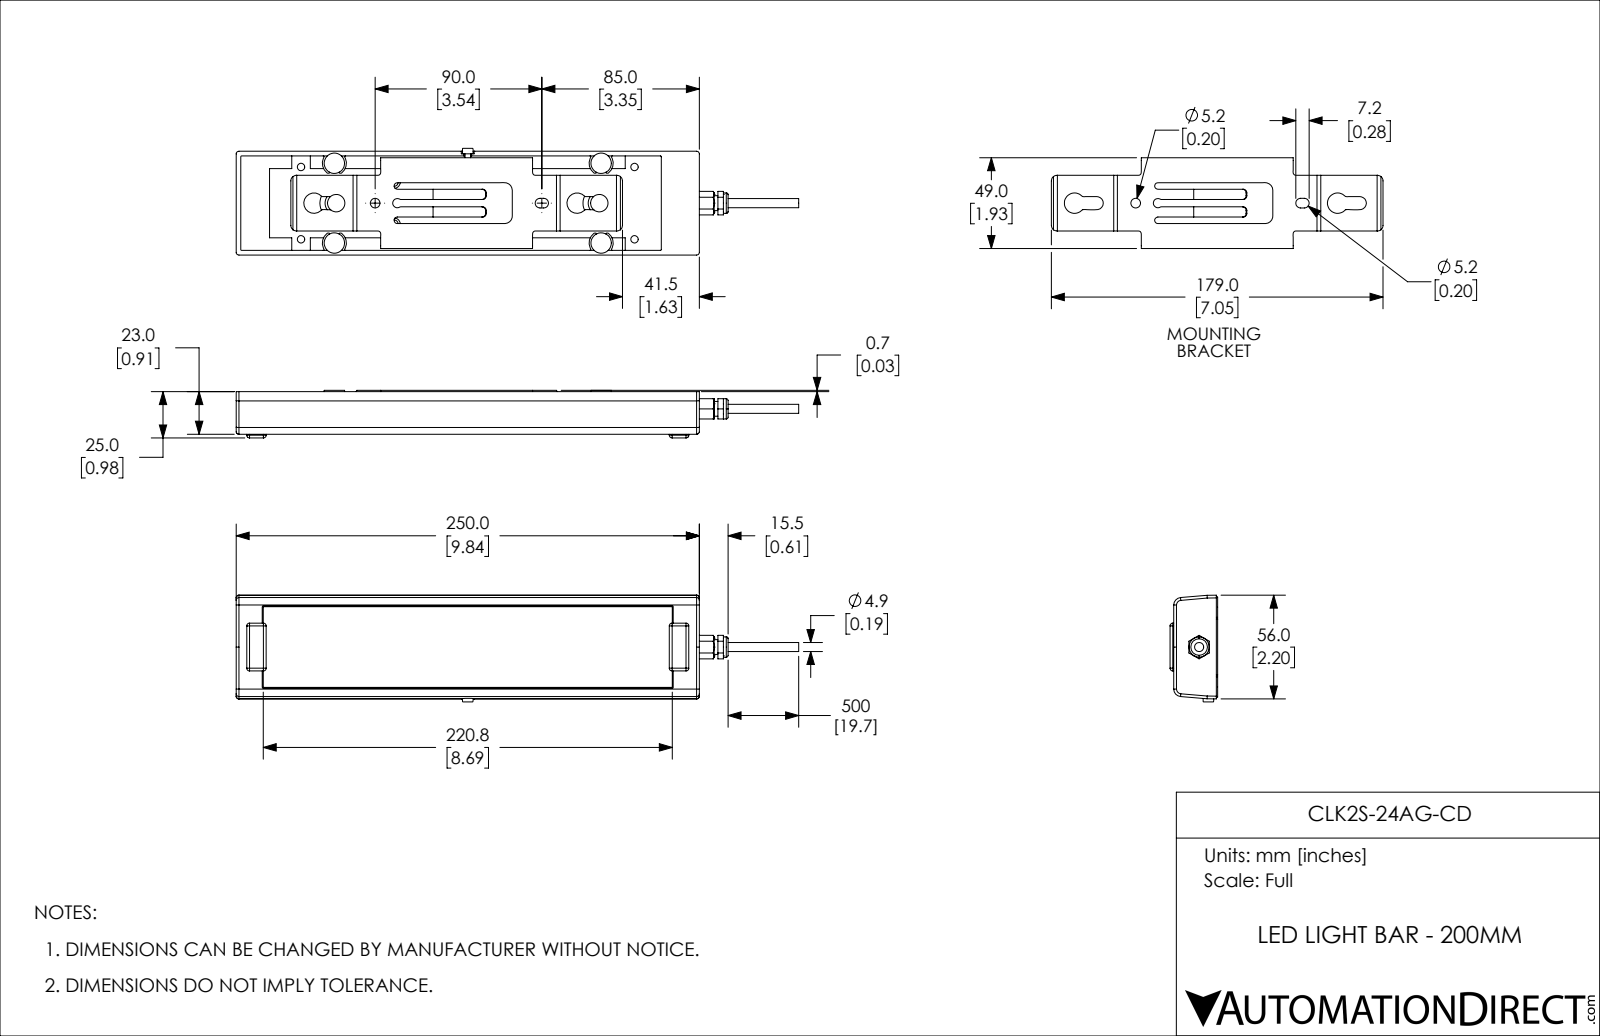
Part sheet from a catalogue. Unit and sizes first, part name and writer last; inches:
Units: inches
Overall size (bounding box): 11.953 × 2.268 × 1.012
Round holes (diameter × count): ⌀0.157 ×4, ⌀0.118 ×1, ⌀0.205 ×1
Round bosses / shafts (diameter × count): ⌀0.433 ×5, ⌀0.37 ×2, ⌀0.256 ×2, ⌀0.315 ×1, ⌀0.193 ×1
Partial cylindrical surfaces — rounded edges, fillets, slot ends (radius × count): R0.059 ×22, R0.079 ×4, R0.02 ×2, R0.102 ×2, R0.157 ×2
Main face-to-face distances: 0.697, 0.059, 0.236, 0.933, 0.874, 0.177, 0.269, 1.739, 0.138, 0.039
Hole centre spacings: 1.535, 1.752, 5.565, 7.087, 7.251
Volume: 14.4 in³ · Surface area: 112.7 in²
Bodies: 5 solids, 303 faces (138 planar, 74 cylindrical, 91 other)
Part name (STEP PRODUCT): CLK2S-24AG-CD
STEP written by: SolidWorks 2018 (AUTOMOTIVE_DESIGN)
